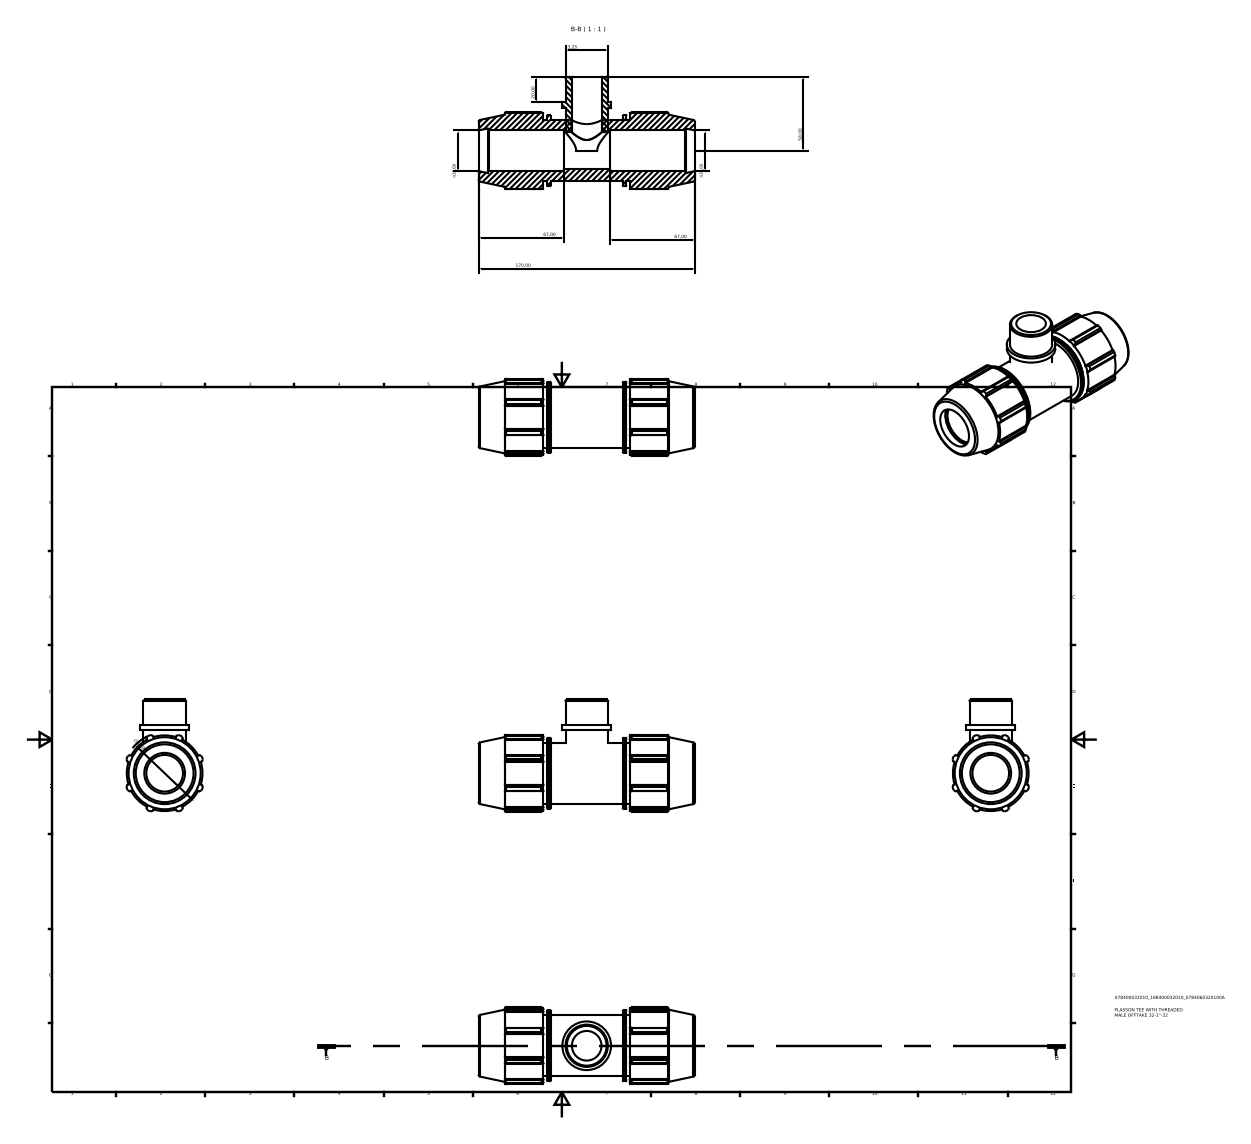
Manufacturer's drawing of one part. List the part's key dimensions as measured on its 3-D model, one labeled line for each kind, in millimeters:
Part name (STEP PRODUCT): 078400032010_188400032010
STEP written by: Autodesk Inventor 2015 (AUTOMOTIVE_DESIGN)
Units: millimetres
Bodies: 2 solids, 158 faces (81 planar, 46 cylindrical, 31 other)
Overall size (bounding box): 170 × 88.11 × 60.22
Volume: 275 308 mm³ · Surface area: 64 639 mm²
Round holes (diameter × count): ⌀23.27 ×1, ⌀28.8 ×1, ⌀32 ×1
Round bosses / shafts (diameter × count): ⌀55.68 ×1, ⌀48 ×1, ⌀38.24 ×1, ⌀33.25 ×1
Partial cylindrical surfaces — rounded edges, fillets, slot ends (radius × count): R29.76 ×1, R32 ×1
Main face-to-face distances: 51, 119, 56.67, 113.33, 5.67, 62.33, 53.83, 116.17, 2.83, 65.17
